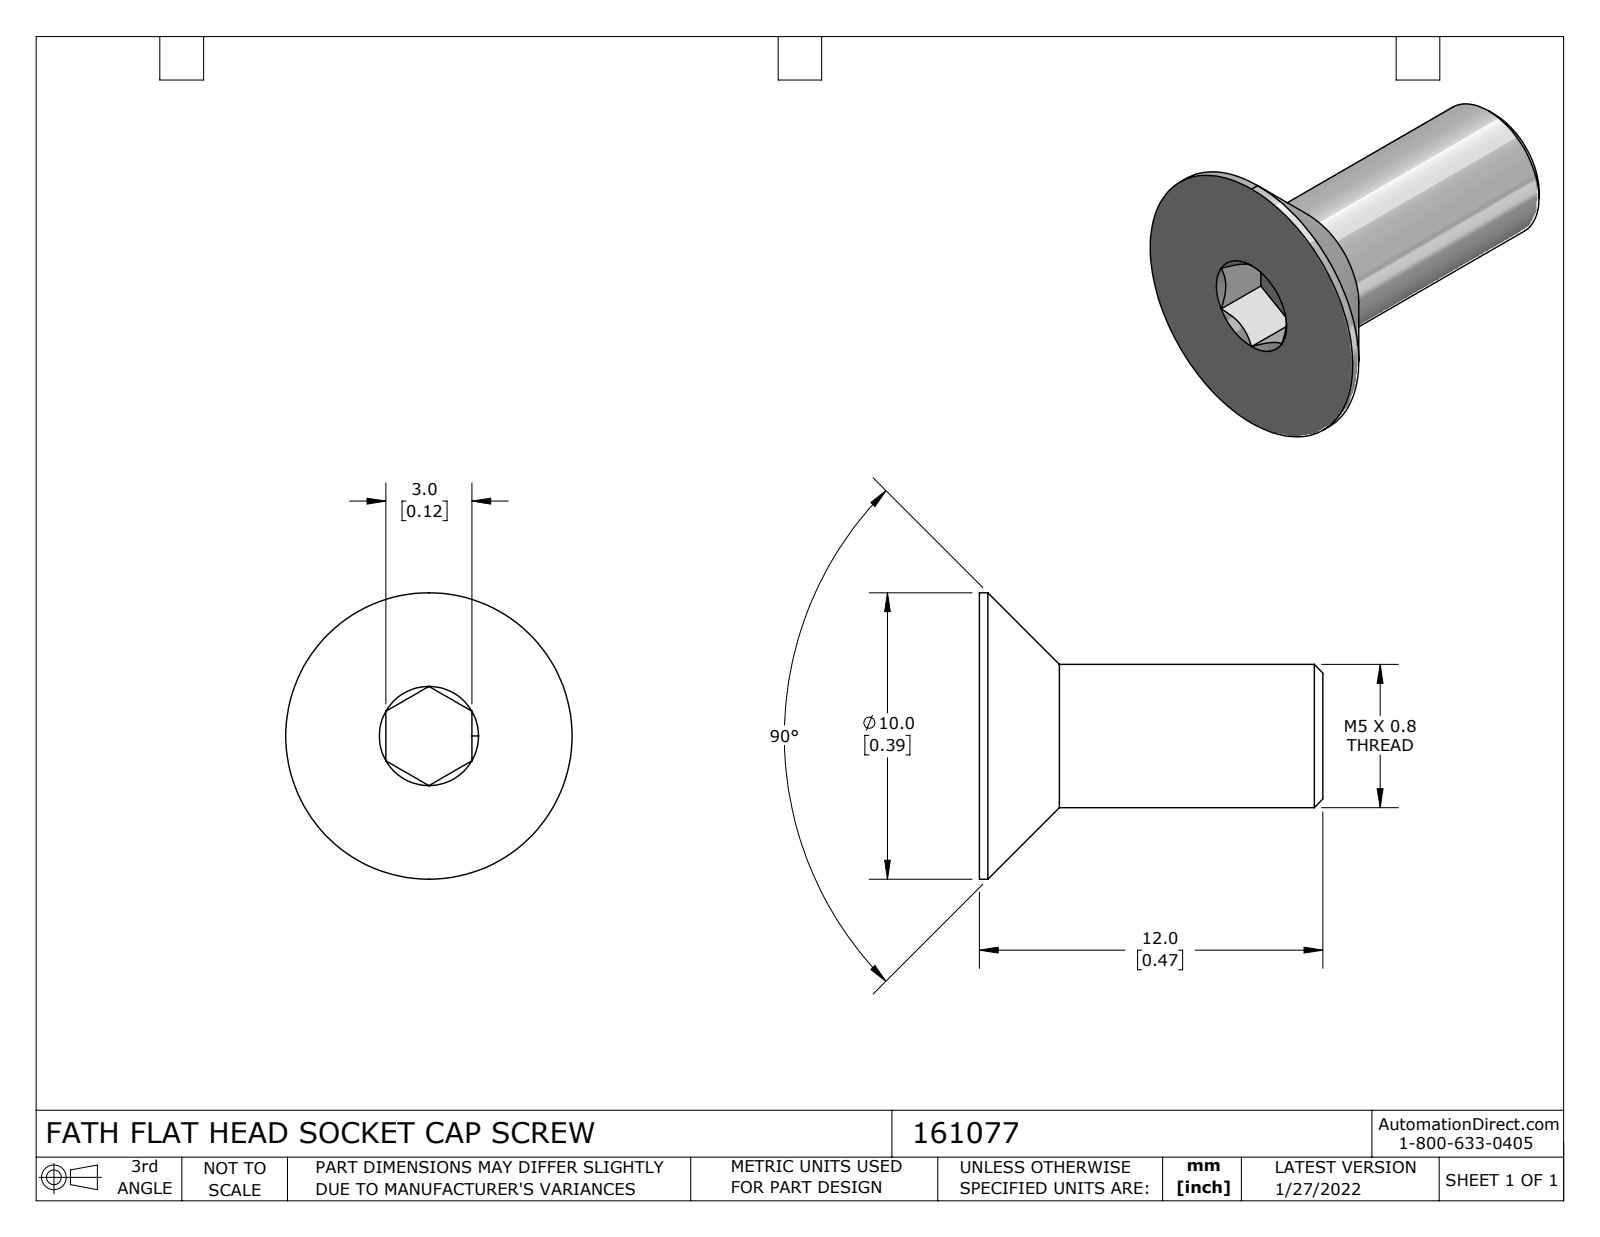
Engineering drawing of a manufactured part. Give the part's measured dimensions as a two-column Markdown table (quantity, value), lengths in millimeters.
| quantity | value |
| --- | --- |
| part name | 161077 |
| STEP written by | SolidWorks 2021 (CONFIG_CONTROL_DESIGN) |
| units | millimeters |
| bodies | 1 solid, 24 faces (9 planar, 4 cylindrical, 11 other) |
| overall size | 12 × 10 × 10 |
| volume | 303 mm³ |
| surface area | 352 mm² |
| round bosses / shafts (diameter × count) | 10 × 1, 5 × 1 |
| main face-to-face distances | 12, 3, 10.04, 1.96 |
